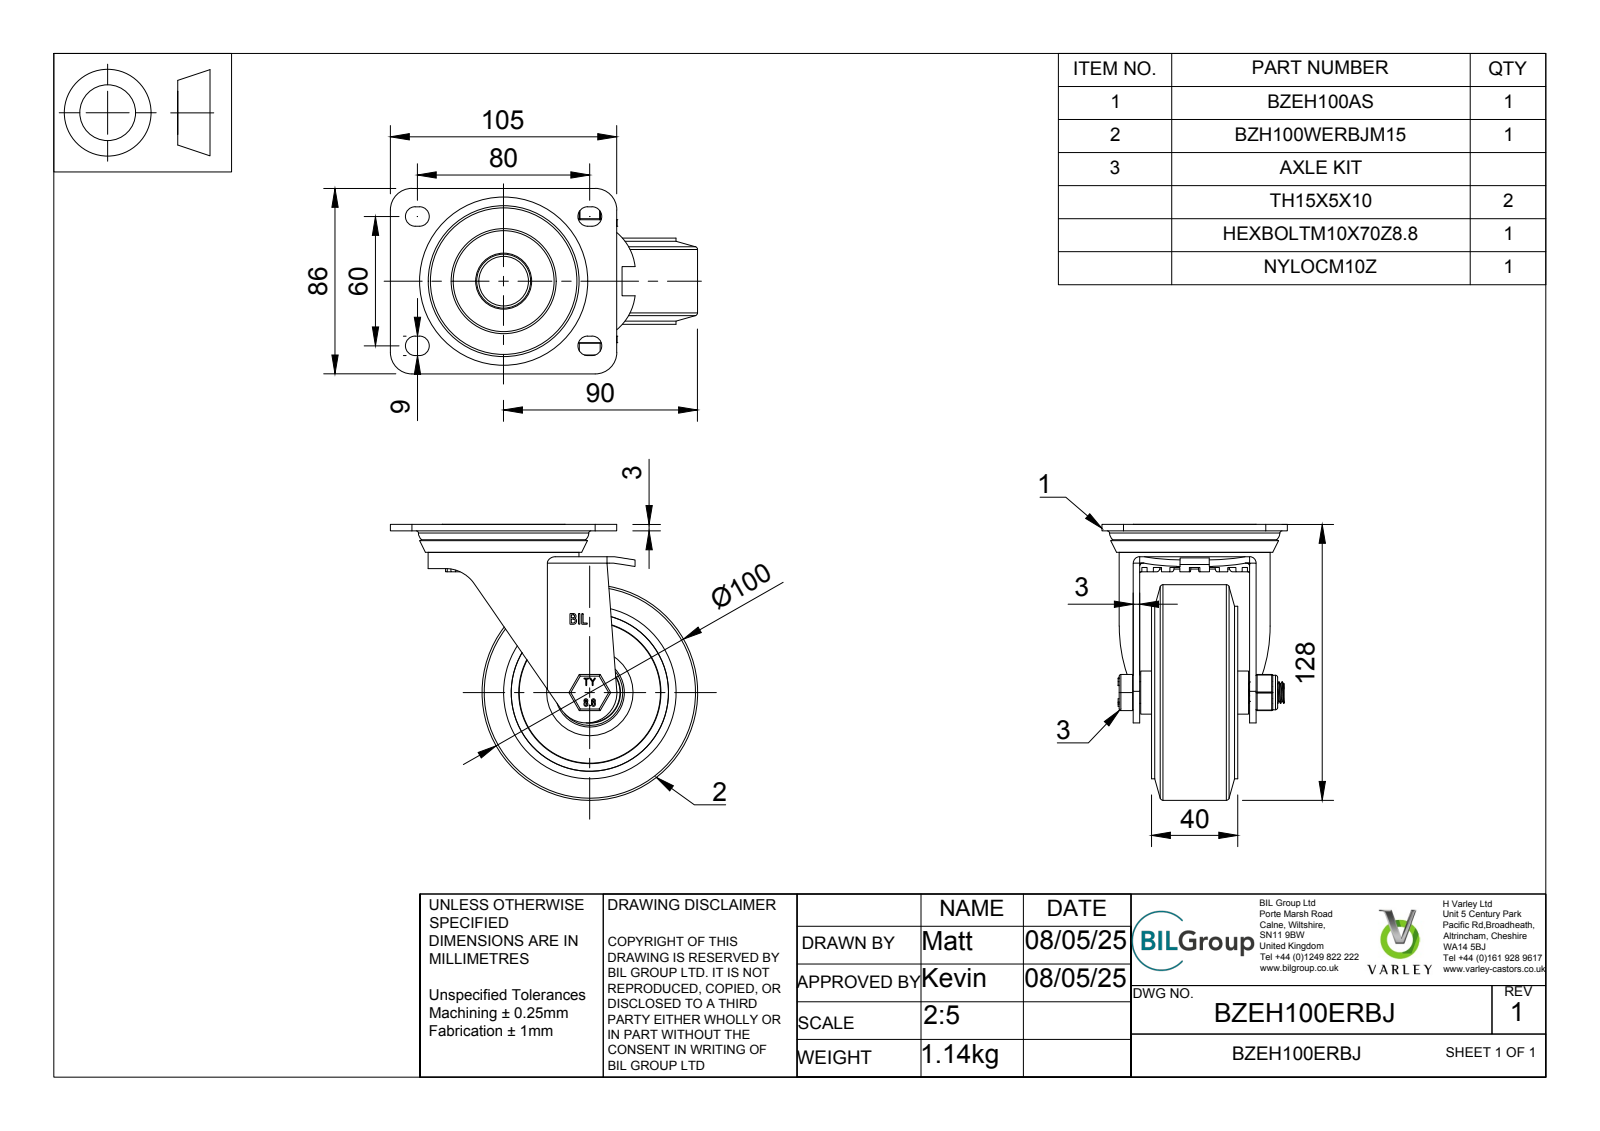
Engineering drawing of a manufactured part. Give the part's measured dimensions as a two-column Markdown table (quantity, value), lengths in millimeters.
| quantity | value |
| --- | --- |
| part name | BZEH100ERBJ v3; BZEH100AS - 2 v2; ZINC PLATED, PRESSED STEEL TOP PLATE; ZINC PLATED, PRESSED STEEL TOP PLATE Geometry (+7 more) |
| STEP written by | Autodesk Translation Framework v14.4.0.0 (AUTOMOTIVE_DESIGN) |
| units | millimeters |
| bodies | 59 solids, 1218 faces (563 planar, 192 cylindrical, 463 other) |
| overall size | 142.5 × 128 × 86 |
| volume | 318 715 mm³ |
| surface area | 141 609 mm² |
| round holes (diameter × count) | 10 × 1, 10.2 × 1, 10.5 × 1, 12 × 1, 15 × 1, 18 × 1, 20 × 1, 21 × 1, 27.4 × 1, 30 × 1, 32 × 1, 64 × 1 |
| round bosses / shafts (diameter × count) | 100 × 1, 80 × 1, 70 × 1, 54 × 1, 40 × 1, 28.4 × 1, 28 × 1, 25 × 1 |
| partial cylindrical surfaces (radius × count) | 0.5 × 18, 4.5 × 8, 0.75 × 6, 10 × 4, 1.25 × 3, 3 × 2, 24.04 × 2, 11.47 × 1 |
| main face-to-face distances | 3, 5, 8, 7, 10, 8.5, 2, 16, 54, 48.5 |
